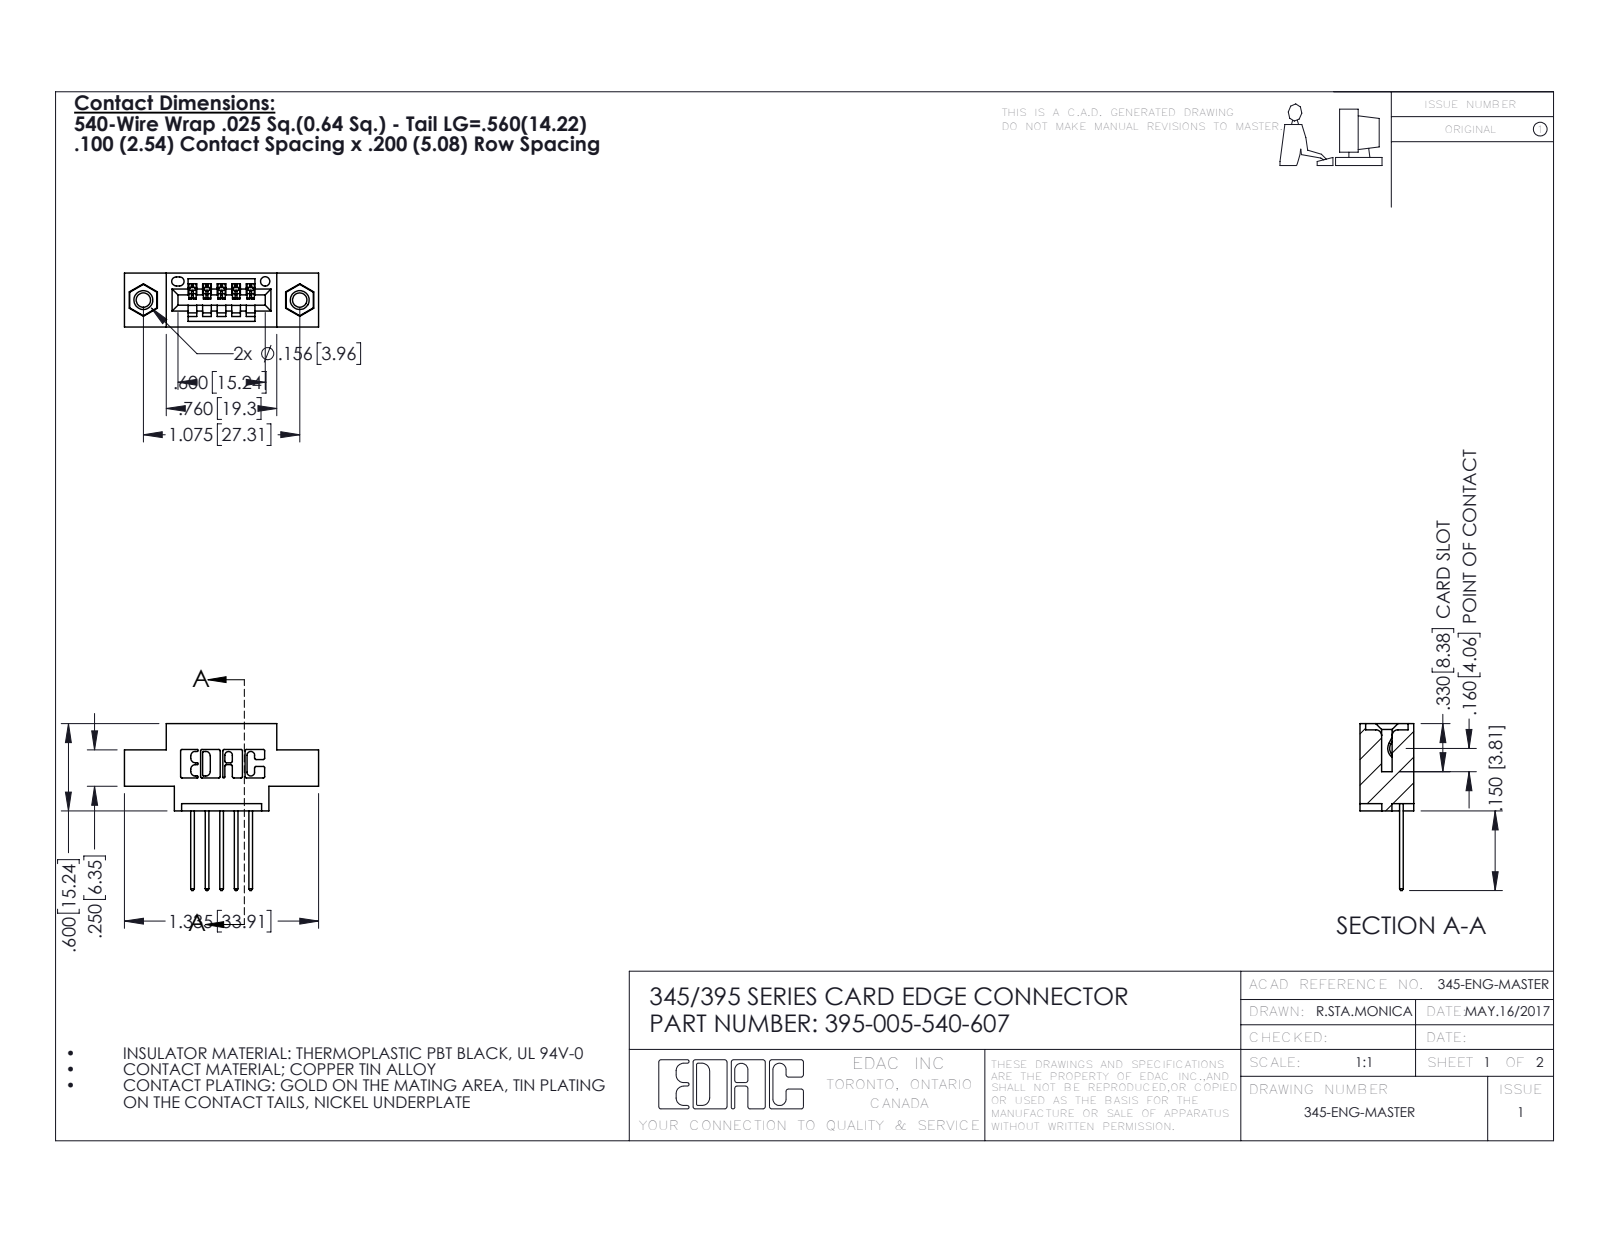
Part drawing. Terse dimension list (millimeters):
name: 345-250-001_345-250-005-103; 345-292-001_345-293-140; 395-005-540-607; 345 Part_0.170 Offset - 0.156 Dia-TI
written by: SolidWorks 2016 (CONFIG_CONTROL_DESIGN)
unit: mm
bodies: 8 solids, 480 faces (316 planar, 148 cylindrical, 16 other)
size: 33.9 × 29.1 × 9.4
volume: 2 800 mm³; area: 3 423 mm²
holes: 2× ⌀2.5, 2× ⌀3.2, 2× ⌀4, 1× ⌀1.6
bosses: 2× ⌀3.9
rounds: 22× R0.3, 10× R0.2, 10× R0.3, 6× R0.2, 6× R0.8, 3× R0.7, 2× R0.8, 2× R1
face distances: 9.4, 5.1, 1.8, 7.6, 2.5, 0.6, 2.5, 6.9, 6.4, 1.5
hole spacings: 6.9, 21.5, 27.3
